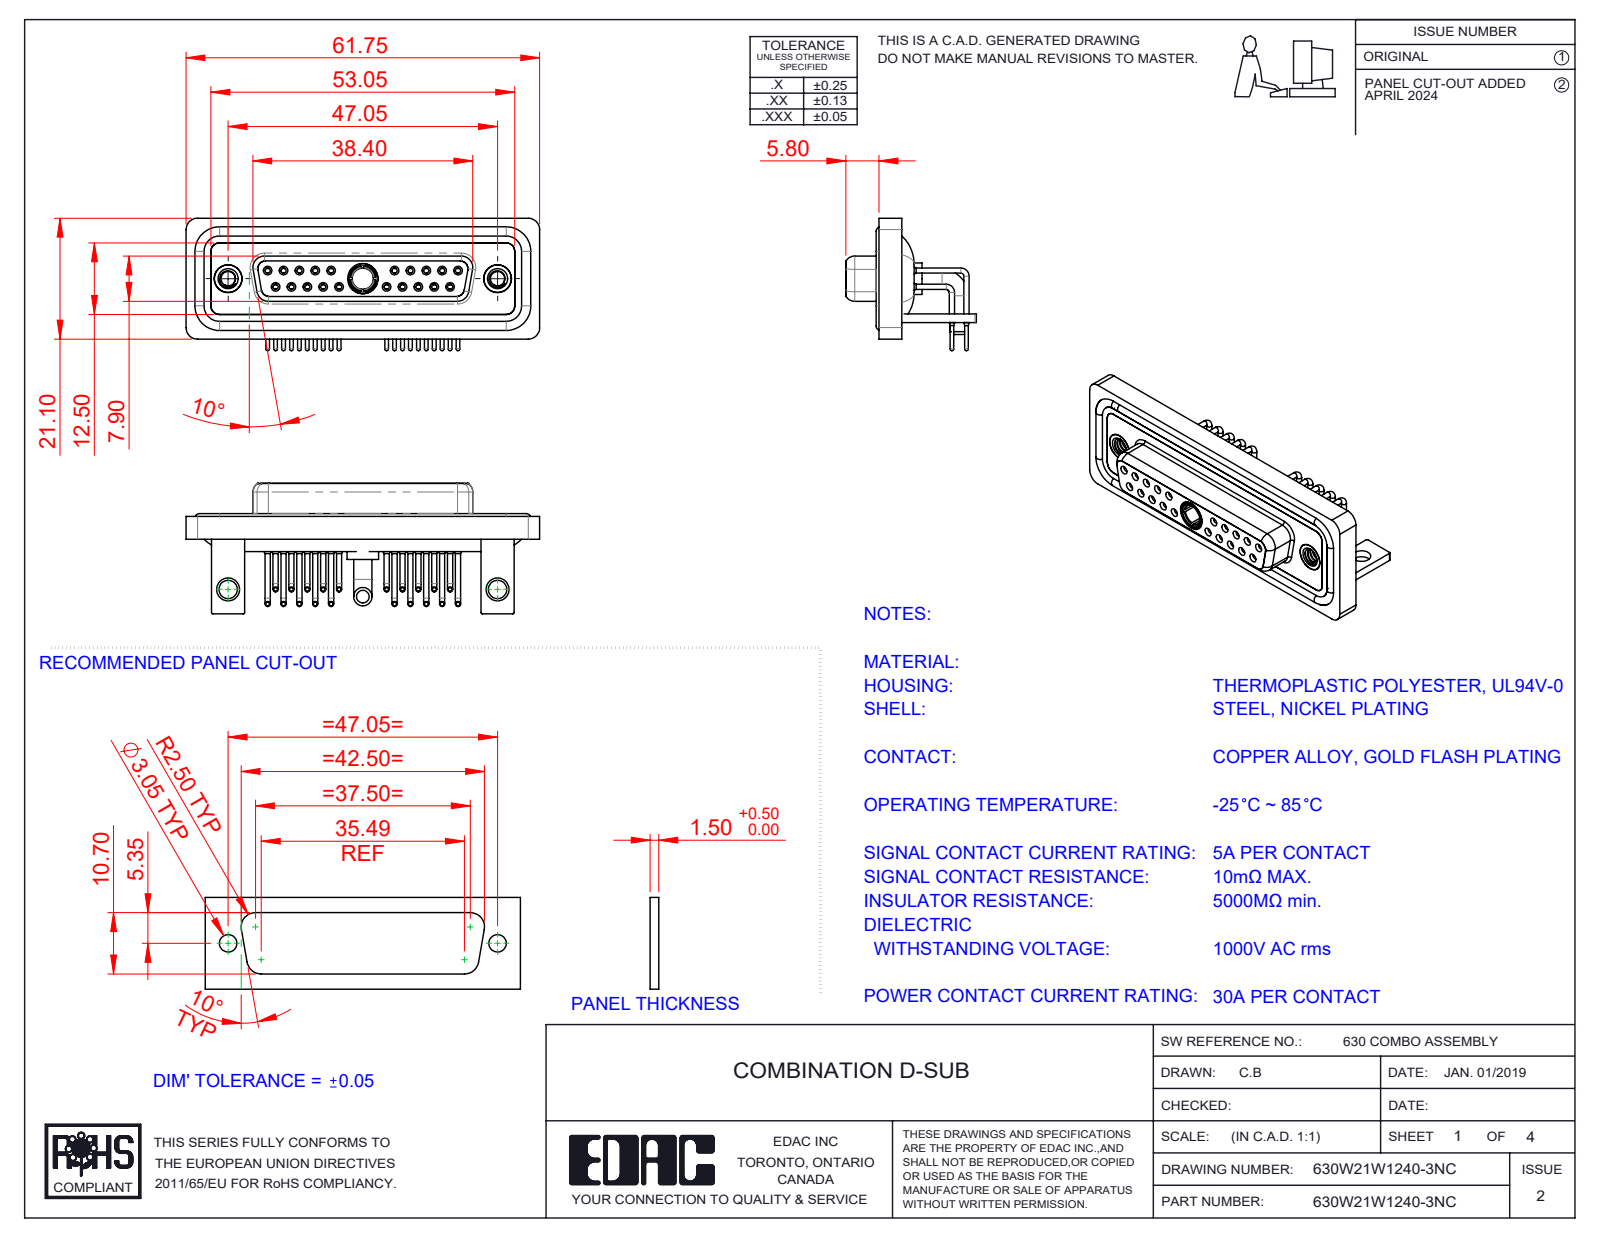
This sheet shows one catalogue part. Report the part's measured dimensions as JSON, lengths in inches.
{"part_name": "630Combo Housing_21W1; 630Combo Stabilizer Bracket_50 Contacts; 630Combo Contact Row 1_50 Contacts; 630Combo Waterproof Housing_25 Contacts (+6 more)", "step_written_by": "SolidWorks 2023 (CONFIG_CONTROL_DESIGN)", "units": "inches", "bodies": {"solids": 31, "faces": 1566, "planar": 454, "cylindrical": 695, "other": 417}, "overall_size": [2.431, 0.91, 0.898], "volume_in3": 0.543, "surface_area_in2": 24.08, "round_holes": [[0.035, 20], [0.043, 20], [0.059, 20], [0.079, 20], [0.063, 10], [0.067, 10], [0.191, 3], [0.098, 2], [0.126, 2], [0.157, 2], [0.159, 2], [0.197, 2]], "round_bosses_or_shafts": [[0.035, 20], [0.026, 20], [0.063, 14], [0.195, 2], [0.189, 2], [0.126, 2], [0.217, 1], [0.205, 1]], "partial_cylinders_radius": [[0.079, 19], [0.059, 18], [0.01, 16], [0.053, 8], [0.063, 8], [0.02, 5], [0.024, 4], [0.026, 4]], "face_to_face_distances": [0.016, 0.071, 0.114, 0.146, 0.059, 0.161, 0.043, 0.055, 0.063, 0.098], "hole_center_spacings": [0.124, 0.109, 0.218, 0.327, 0.198, 0.763, 0.826, 0.872]}
